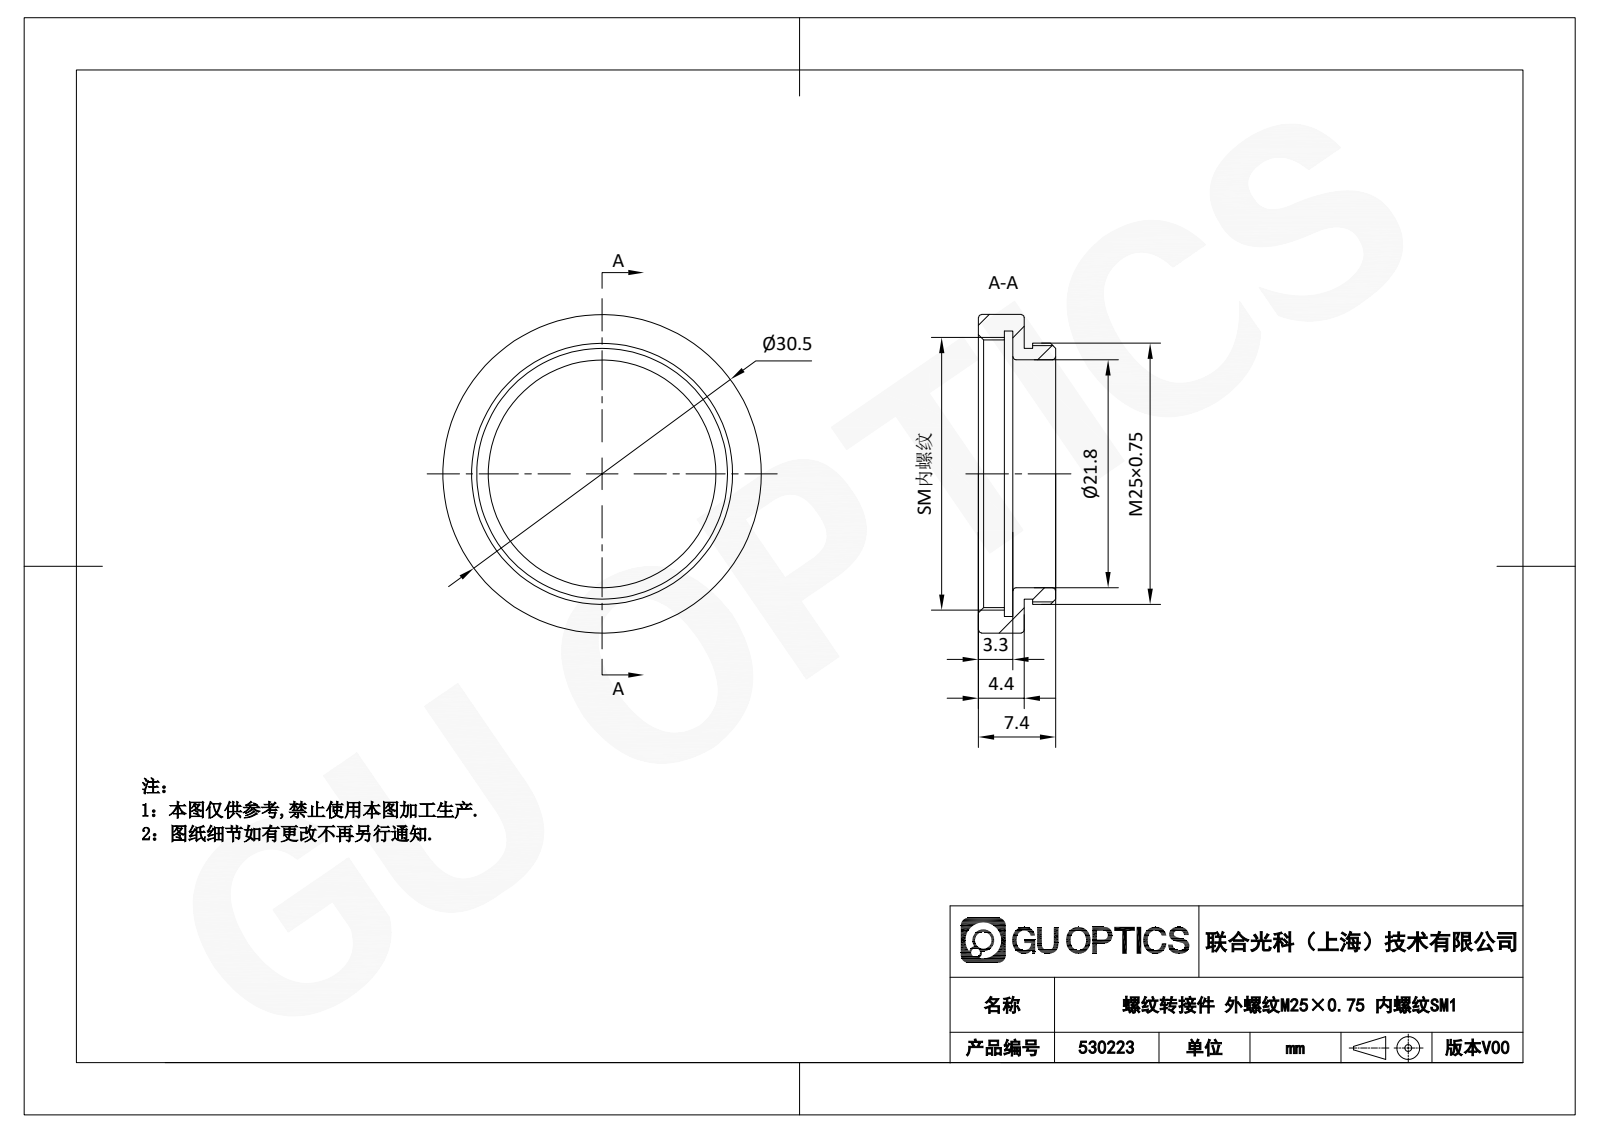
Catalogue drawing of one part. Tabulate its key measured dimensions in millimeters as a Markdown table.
| quantity | value |
| --- | --- |
| part name | 530223 |
| STEP written by | SolidWorks 2020 (CONFIG_CONTROL_DESIGN) |
| units | millimeters |
| bodies | 1 solid, 18 faces (6 planar, 6 cylindrical, 6 other) |
| overall size | 30.5 × 30.5 × 7.4 |
| volume | 1 346 mm³ |
| surface area | 2 049 mm² |
| round holes (diameter × count) | 21.8 × 1, 25.6 × 1, 27.3 × 1 |
| round bosses / shafts (diameter × count) | 30.5 × 1, 25 × 1, 24 × 1 |
| main face-to-face distances | 1.1, 4.4, 3.3, 0.8, 1.9, 2.5, 3, 4.1, 4.9, 7.4 |
